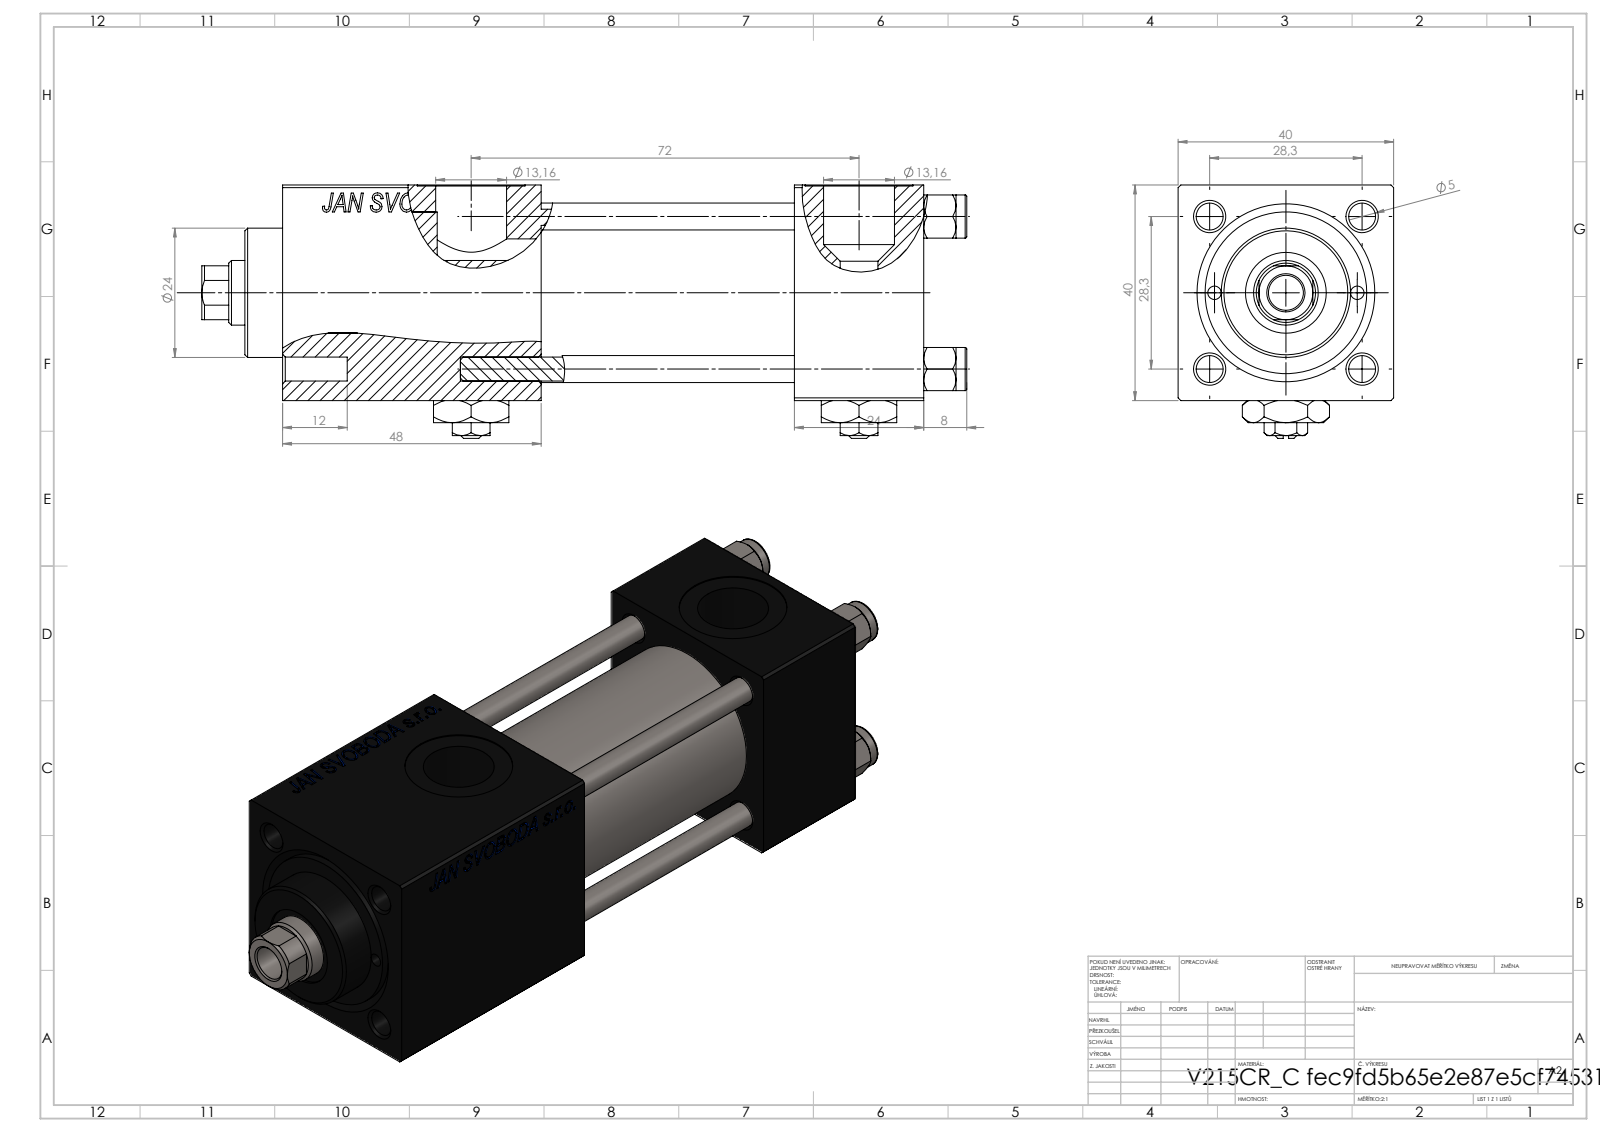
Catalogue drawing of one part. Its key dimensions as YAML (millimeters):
part_name: "V215_VC_A; Zatka_pro_OIL_PORT; V215CR_VCP_C; V215CR_C_Body (+2 more)"
step_written_by: "SolidWorks 2019 (CONFIG_CONTROL_DESIGN)"
units: millimeters
bodies: {solids: 13, faces: 1254, planar: 574, cylindrical: 102, other: 578}
overall_size: [142, 47, 40]
volume: 140534
surface_area: 56353
round_holes:
  - {diameter: 5, count: 4}
  - {diameter: 20, count: 3}
  - {diameter: 2.5, count: 2}
  - {diameter: 7, count: 2}
  - {diameter: 13.16, count: 2}
  - {diameter: 6.5, count: 1}
  - {diameter: 12, count: 1}
  - {diameter: 15, count: 1}
  - {diameter: 25, count: 1}
  - {diameter: 30, count: 1}
round_bosses_or_shafts:
  - {diameter: 8, count: 4}
  - {diameter: 31, count: 1}
  - {diameter: 24, count: 1}
partial_cylinders:
  - {radius: 5.5, count: 1}
face_to_face_distances: [40, 24, 39.8, 90.3, 66.3, 47, 48, 71, 19.3, 95]
hole_center_spacings: [14.18, 20.01, 28.3, 30.84, 13.25, 40.02, 26.5, 72]
